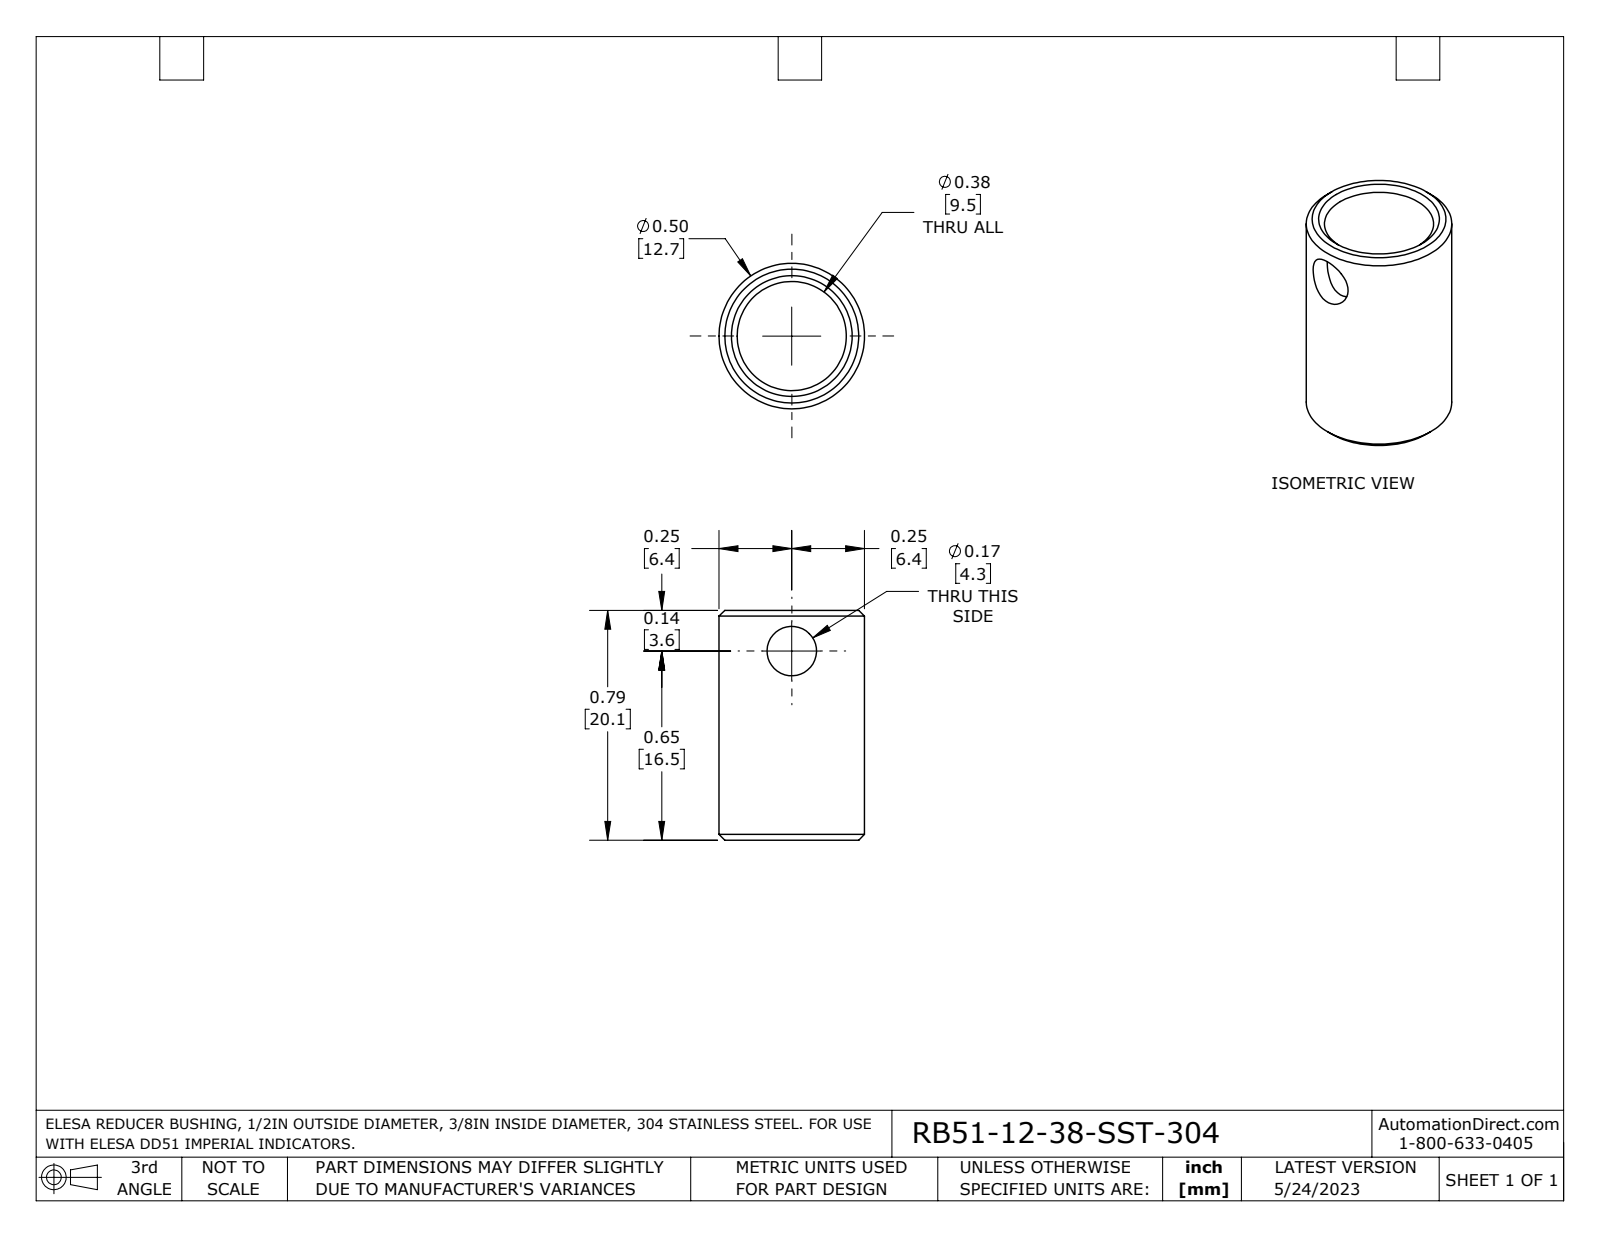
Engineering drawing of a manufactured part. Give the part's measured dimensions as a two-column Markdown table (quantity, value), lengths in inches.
| quantity | value |
| --- | --- |
| part name | RB51-12-38-SST-304 |
| STEP written by | SolidWorks 2021 (AUTOMOTIVE_DESIGN) |
| units | inches |
| bodies | 1 solid, 9 faces (2 planar, 3 cylindrical, 4 other) |
| overall size | 0.79 × 0.5 × 0.5 |
| volume | 0.065 in³ |
| surface area | 2.267 in² |
| round holes (diameter × count) | 0.17 × 1, 0.375 × 1 |
| round bosses / shafts (diameter × count) | 0.5 × 1 |
| main face-to-face distances | 0.79 |
